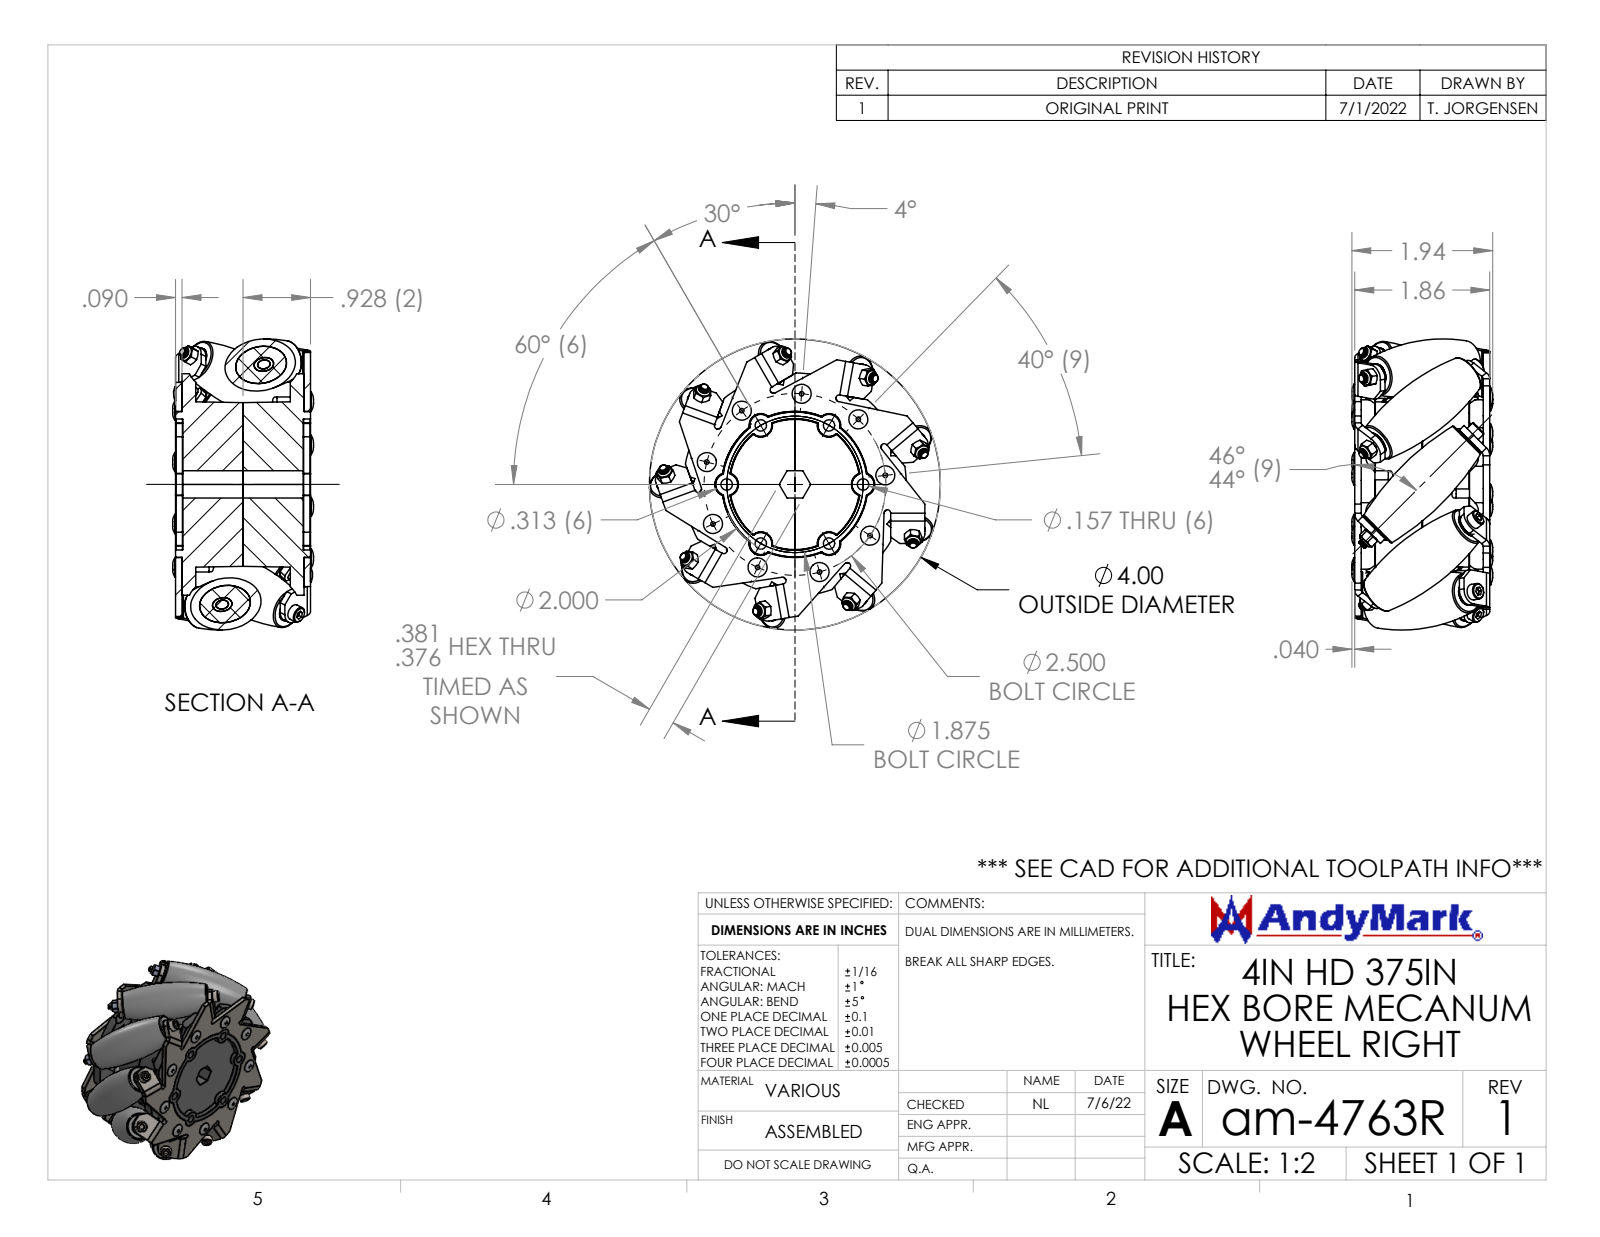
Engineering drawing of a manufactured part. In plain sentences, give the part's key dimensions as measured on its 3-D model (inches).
The part is named "ip-xxxx_half 4HD 375H Mecanum Hub; 4HD Mecanum Roller and Axle; Brass tube; ip-3026R_plate 4 HD Right Mecanum Plate (+6 more)". Its 3-D file was written by "SolidWorks 2022 (CONFIG_CONTROL_DESIGN)". It is 67 solids with 4531 faces: 743 planar, 1474 cylindrical and 2314 other. Overall it measures 4 by 4 by 1.936 inches. Its volume is 12 cubic inches and its surface area 229.6 square inches. Round holes: 42 of diameter 0.135, 18 of diameter 0.063, 16 of diameter 0.135, 9 of diameter 0.123, 9 of diameter 0.125, 9 of diameter 0.187, 6 of diameter 0.157, 2 of diameter 0.252. Round bosses or shafts: 18 of diameter 0.287, 18 of diameter 0.262, 18 of diameter 0.125, 9 of diameter 0.217, 9 of diameter 0.187, 9 of diameter 0.118, 1 of diameter 0.252. Partial cylindrical surfaces (rounded edges, fillets, slot ends): 51 of radius 0.005, 36 of radius 0.219, 28 of radius 0.062, 18 of radius 0.047, 16 of radius 0.188, 15 of radius 0.063, 14 of radius 0.152, 8 of radius 0.163. The main face-to-face distances are 1.676, 0.09, 0.09, 0.928, 1.766, 1.856, 1.766, 0.187, 1.489, 0.1. The hole center spacings are 1.25, 0.855, 0.434, 2.349, 1.607, 1.915, 2.165, 2.462.
